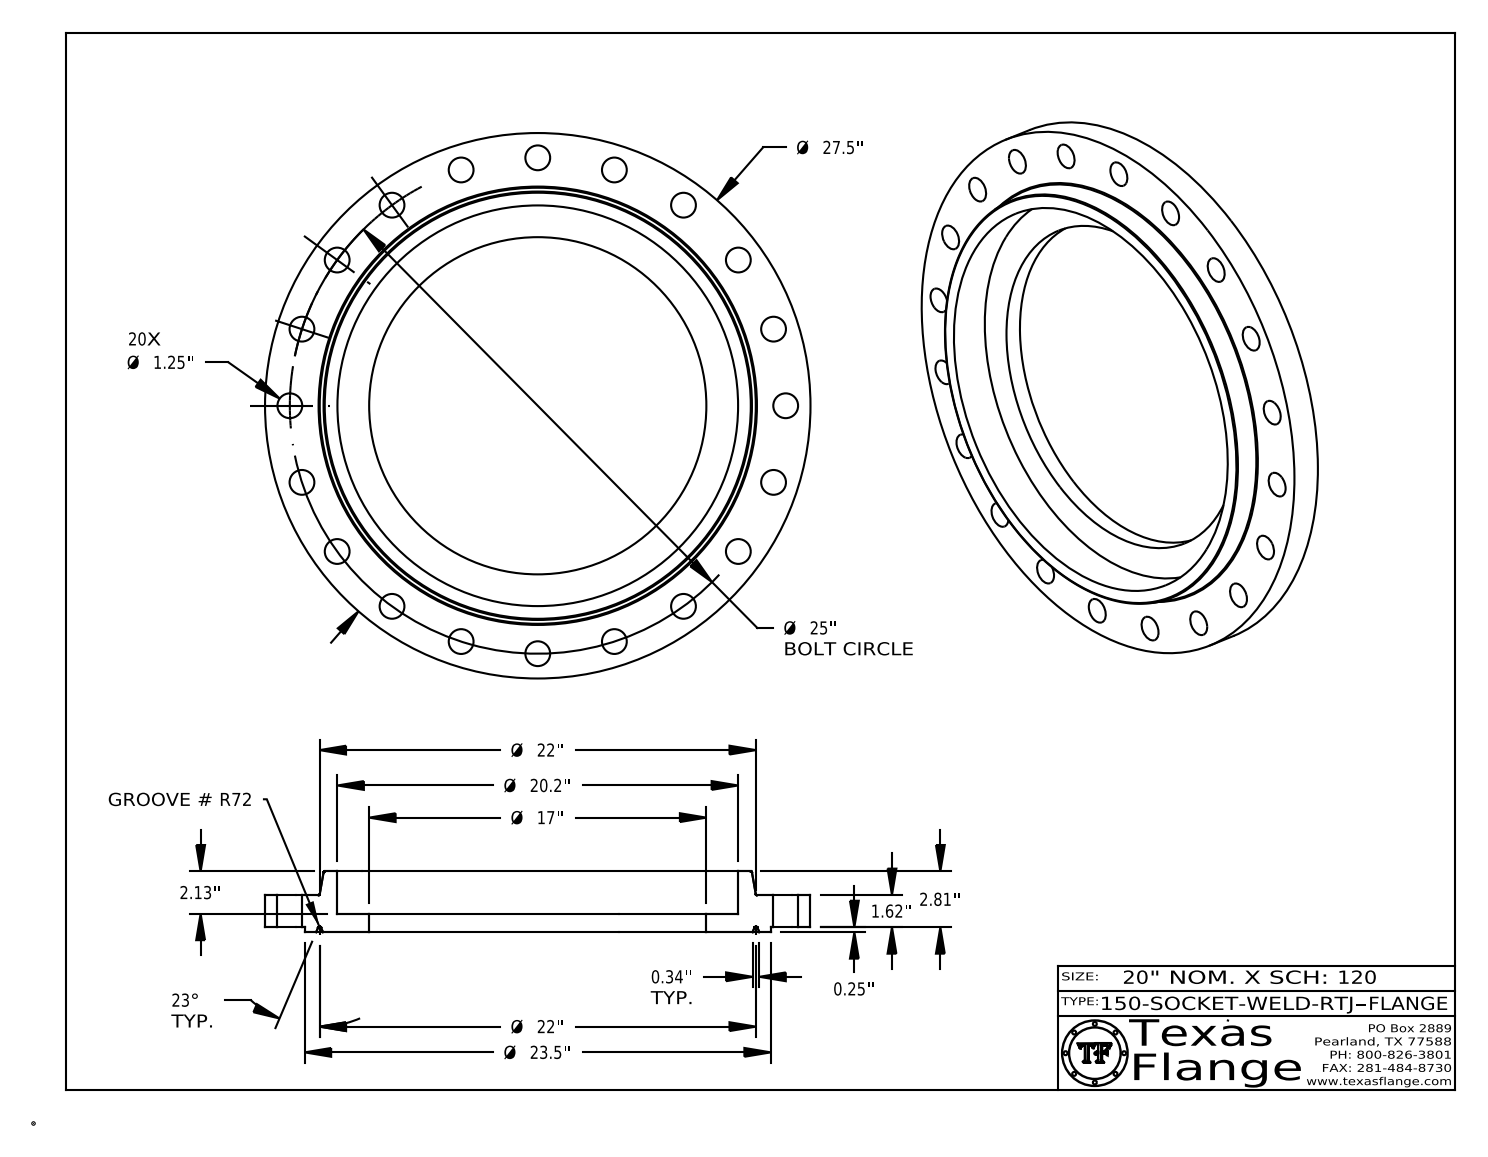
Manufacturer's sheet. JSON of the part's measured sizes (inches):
{"part_name": "150-SOCKET-WELD-RTJ", "step_written_by": "CATIA V5 STEP AP214 (AUTOMOTIVE_DESIGN)", "units": "inches", "bodies": {"solids": 1, "faces": 454, "planar": 372, "cylindrical": 68, "other": 14}, "overall_size": [27.5, 27.5, 3.06], "volume_in3": 576.9, "surface_area_in2": 1244, "round_holes": [[1.25, 20], [0.495, 1], [17, 1], [20.2, 1]], "round_bosses_or_shafts": [[0.03, 8], [27.5, 1], [23.5, 1], [0.39, 1]], "face_to_face_distances": [1.87, 0.25, 1.62, 0.93, 0.68, 0.94, 3.06, 2.81, 2.13, 1.19], "hole_center_spacings": [12.5, 14.694, 17.678, 20.225, 23.776, 24.692, 11.35, 22.275]}
